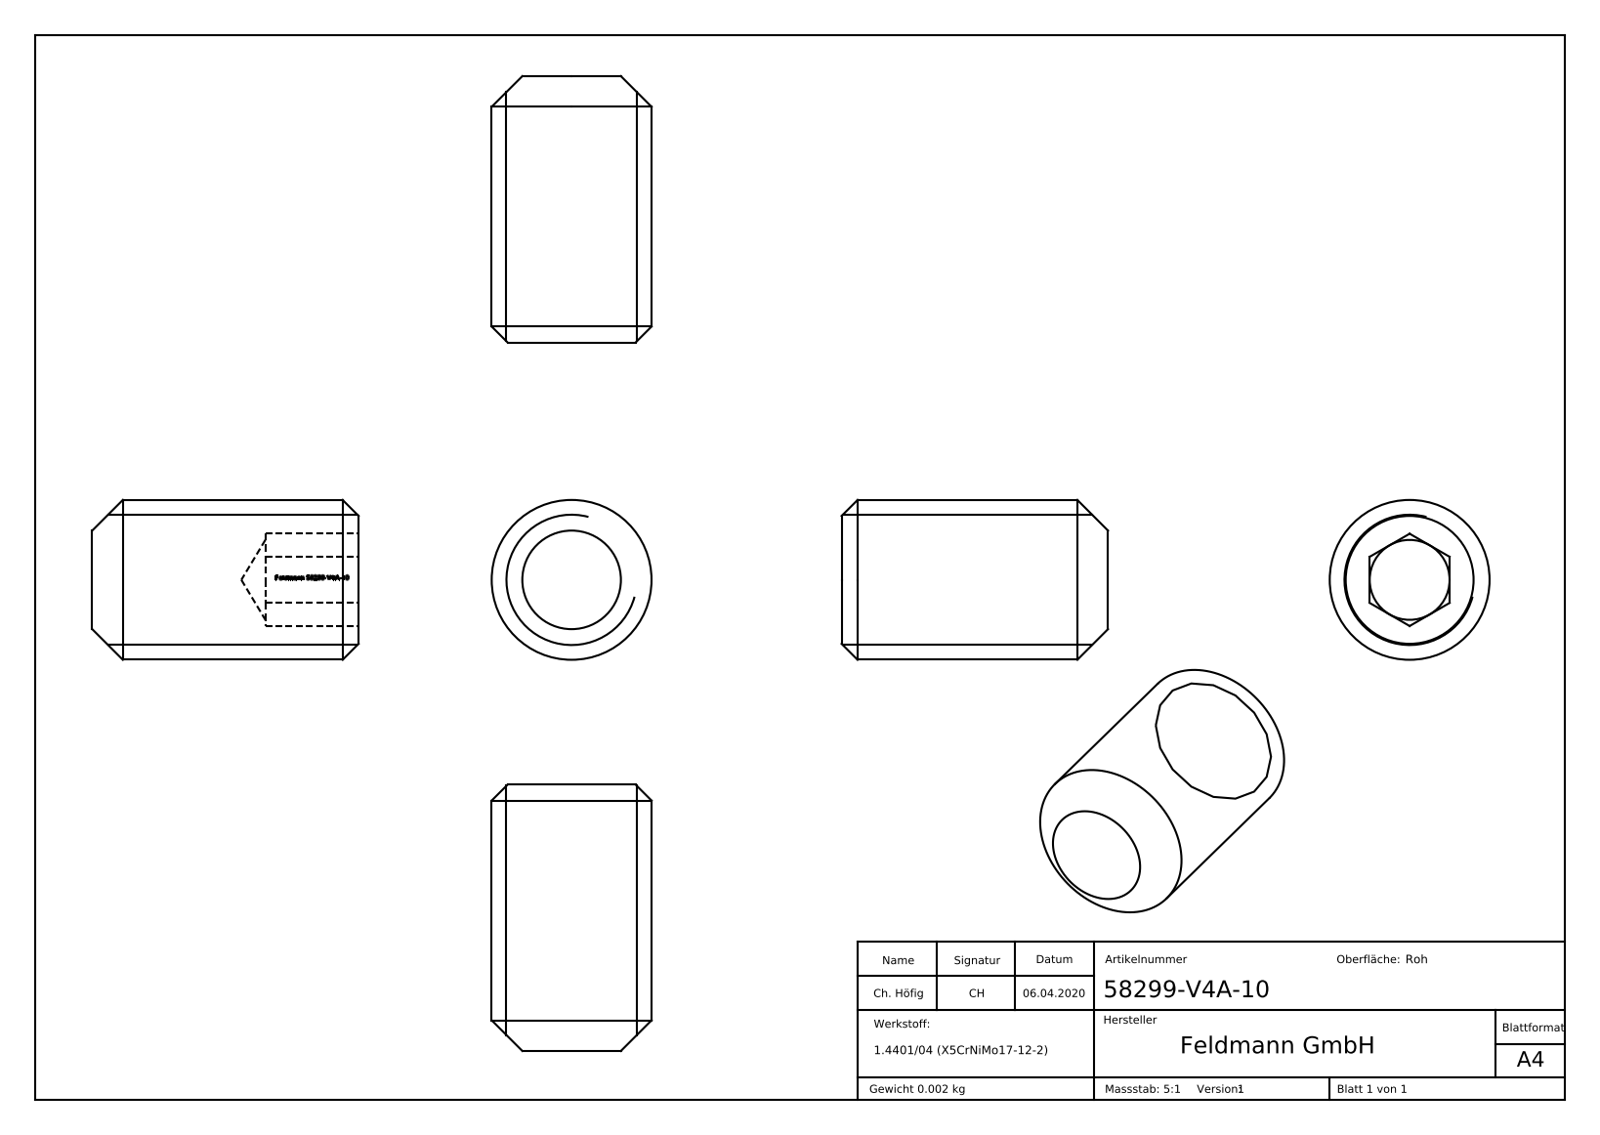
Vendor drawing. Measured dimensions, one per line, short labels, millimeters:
name: 58299-V4A-10
written by: SolidWorks 2015 (CONFIG_CONTROL_DESIGN)
unit: mm
bodies: 1 solid, 290 faces (155 planar, 1 cylindrical, 134 other)
size: 70 × 6 × 6
volume: 239 mm³; area: 263 mm²
bosses: 1× ⌀6
face distances: 3, 10, 6.5, 3.5, 3.1, 0.54, 0.38, 0.4, 0.83, 0.35
